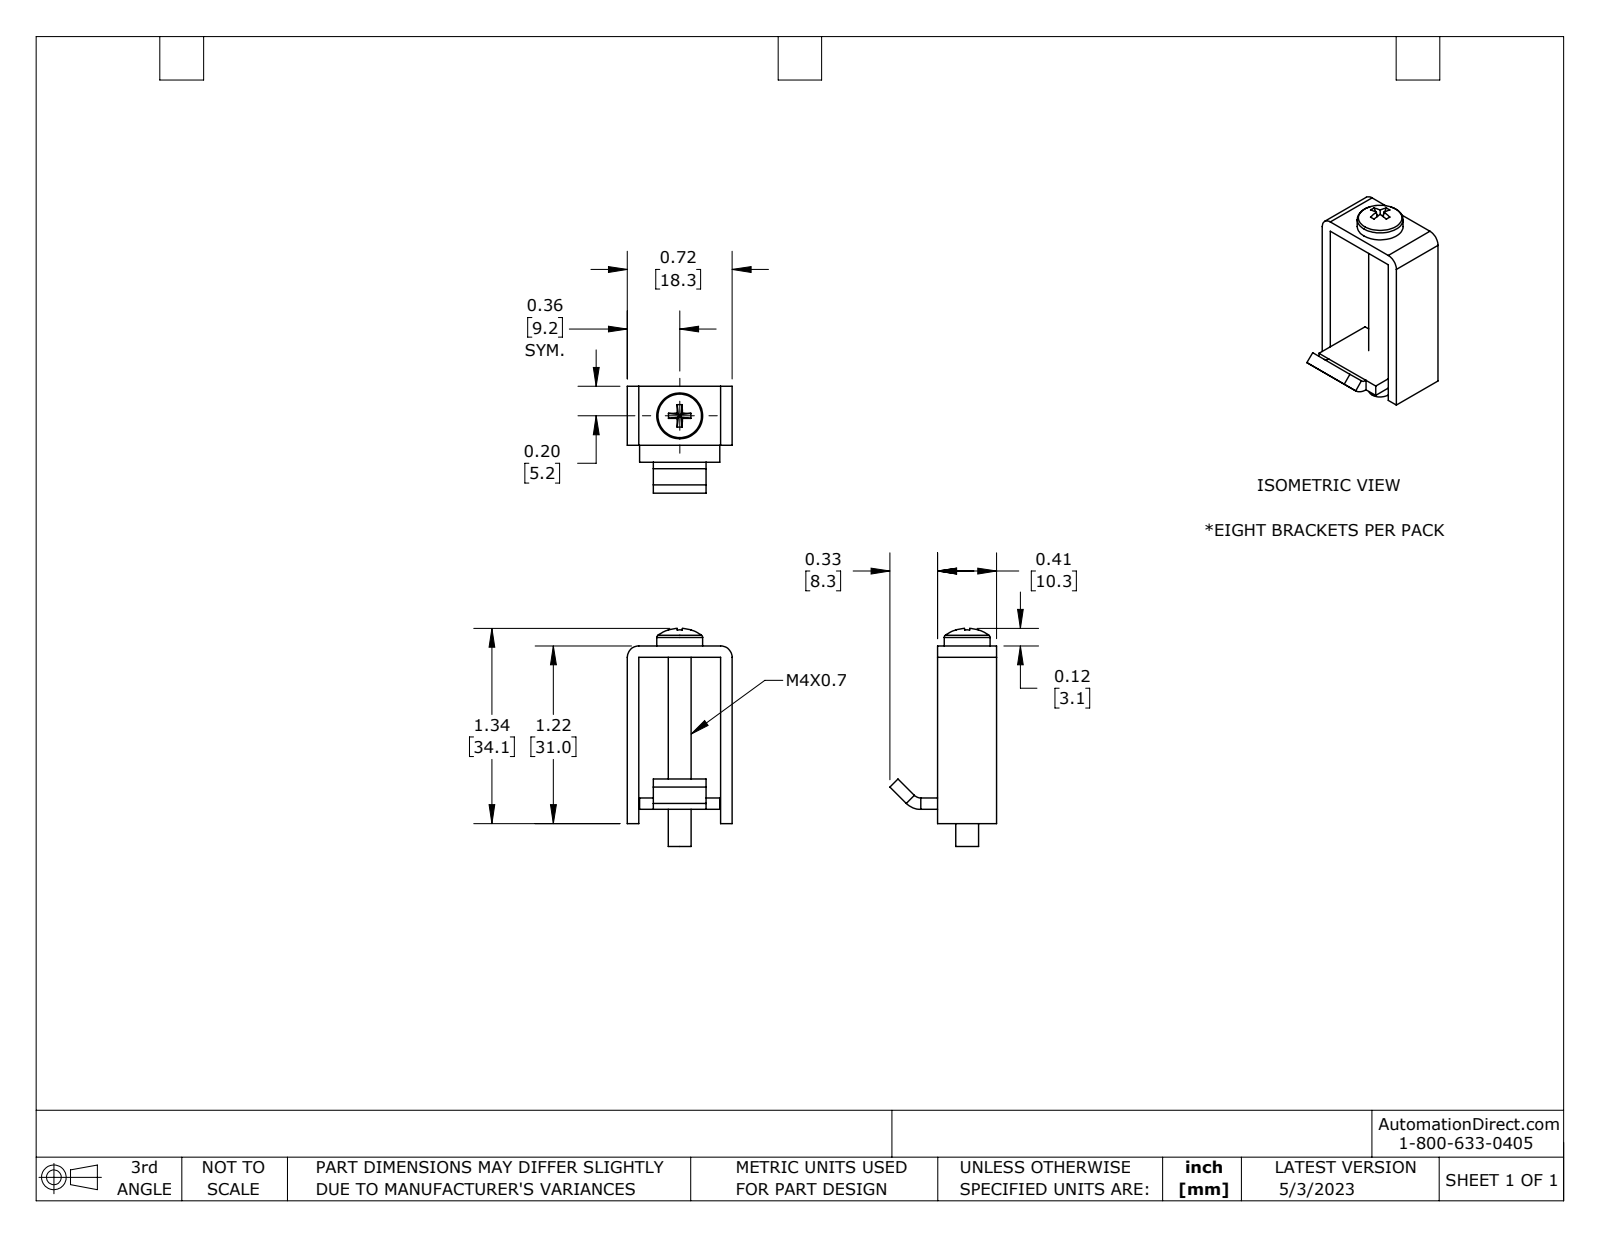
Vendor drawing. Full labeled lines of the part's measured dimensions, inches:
Part name (STEP PRODUCT): HMI-BRK-2
STEP written by: SolidWorks 2021 (AUTOMOTIVE_DESIGN)
Units: inches
Bodies: 3 solids, 48 faces (38 planar, 8 cylindrical, 2 other)
Overall size (bounding box): 1.499 × 0.733 × 0.72
Volume: 0.153 in³ · Surface area: 4.748 in²
Round holes (diameter × count): ⌀0.13 ×1, ⌀0.138 ×1
Round bosses / shafts (diameter × count): ⌀0.315 ×1, ⌀0.157 ×1
Partial cylindrical surfaces — rounded edges, fillets, slot ends (radius × count): R0.079 ×2, R0.063 ×1, R0.141 ×1
Main face-to-face distances: 0.079, 0.642, 0.72, 0.563, 1.044, 0.406, 1.123, 0.966, 0.085, 0.636
